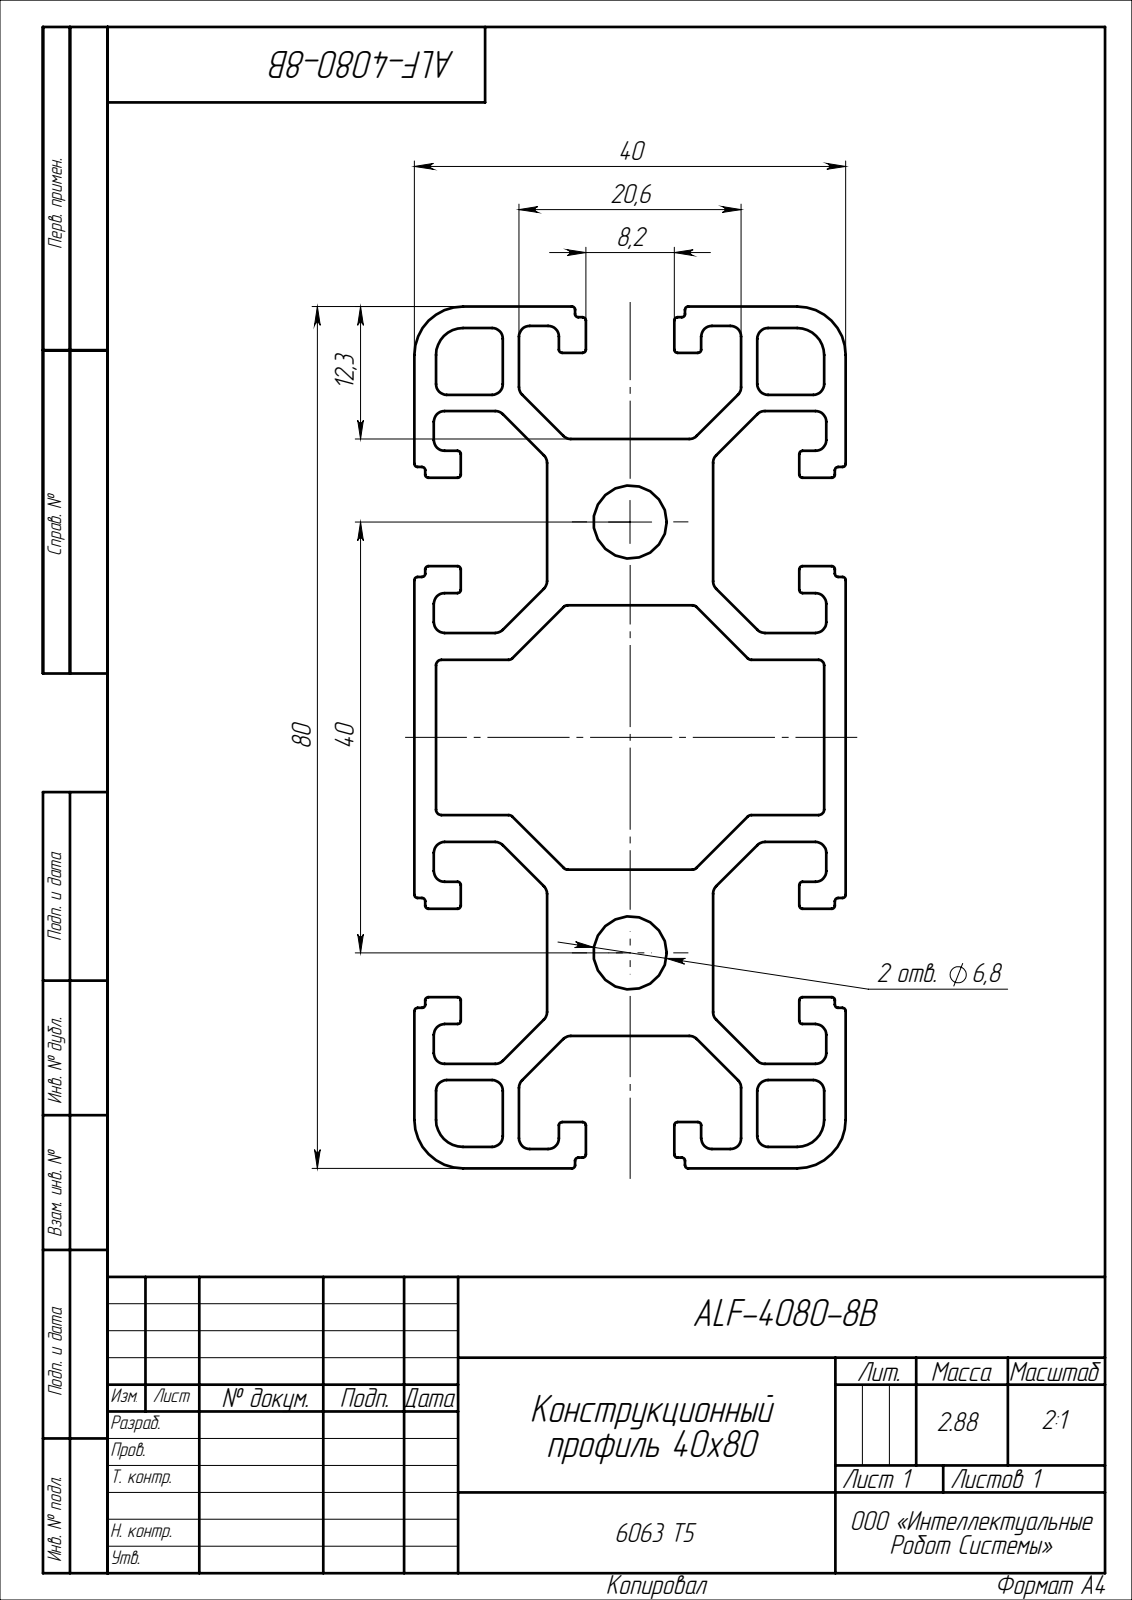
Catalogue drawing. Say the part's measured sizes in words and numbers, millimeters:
The part is named "ALF-4080-8B". Its 3-D file was written by "SolidWorks 2022 (CONFIG_CONTROL_DESIGN)". It is 1 solid with 286 faces: 142 planar, 144 cylindrical and 0 other. Overall it measures 1000 by 80 by 40 millimeters. Its volume is 1 071 000 cubic millimeters and its surface area 781 471 square millimeters. Round holes: 2 of diameter 6.8. Partial cylindrical surfaces (rounded edges, fillets, slot ends): 60 of radius 0.3, 60 of radius 1, 12 of radius 0.5, 4 of radius 2.5, 4 of radius 4.5. The main face-to-face distances are 40, 12.3, 2.5, 6.2, 22.1, 7.7, 8.2, 2, 10.3, 14.4. The hole center spacings are 40.
